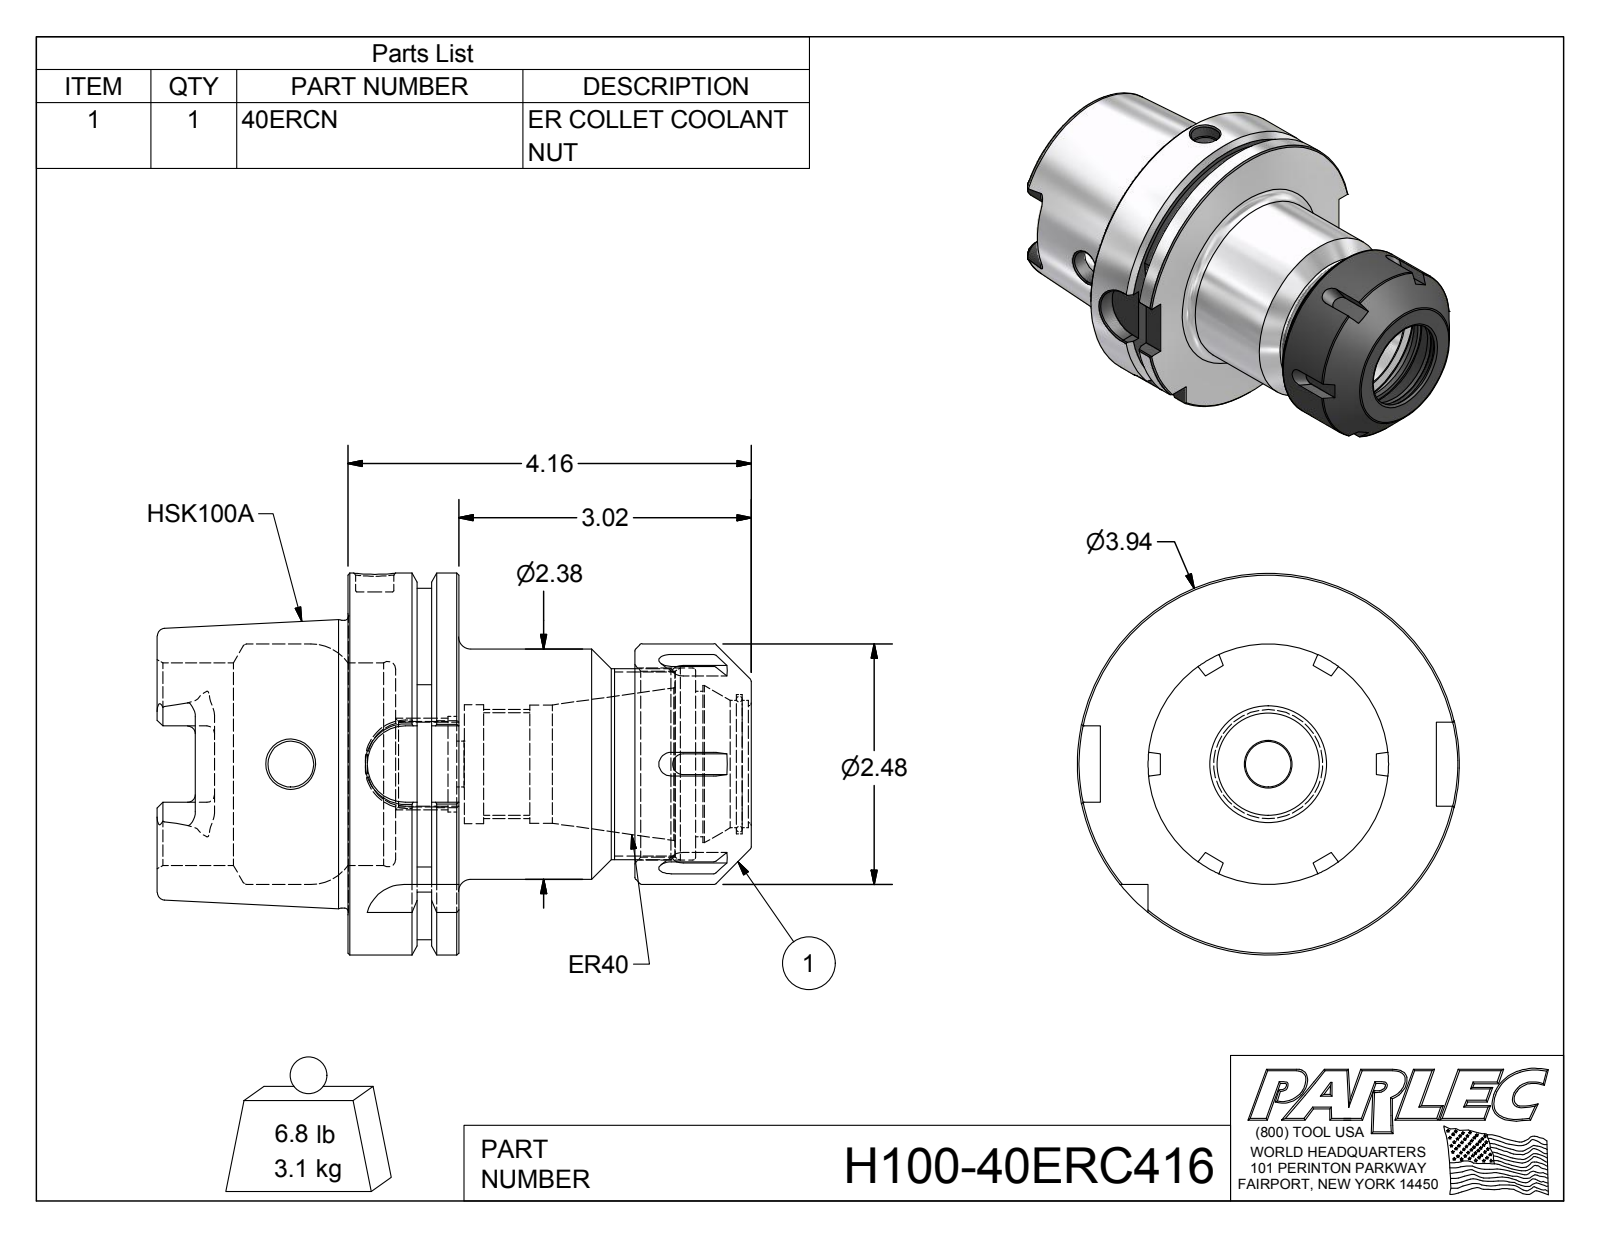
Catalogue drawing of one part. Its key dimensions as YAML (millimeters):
part_name: "H100-40ERC416; H100-40ER4-1; 40ERCN"
step_written_by: "Autodesk Inventor 2012 (AUTOMOTIVE_DESIGN)"
units: millimeters
bodies: {solids: 2, faces: 189, planar: 71, cylindrical: 44, other: 74}
overall_size: [155.7, 100, 100]
volume: 391200
surface_area: 79420
round_holes:
  - {diameter: 12, count: 2}
  - {diameter: 10, count: 1}
  - {diameter: 22.4, count: 1}
  - {diameter: 25, count: 1}
  - {diameter: 26.8, count: 1}
  - {diameter: 31, count: 1}
  - {diameter: 31.1, count: 1}
  - {diameter: 33.4, count: 1}
  - {diameter: 36.5, count: 1}
  - {diameter: 38.1, count: 1}
  - {diameter: 41.1, count: 1}
  - {diameter: 48.7, count: 1}
round_bosses_or_shafts:
  - {diameter: 100, count: 1}
  - {diameter: 75.4, count: 1}
  - {diameter: 63, count: 1}
  - {diameter: 60.3, count: 1}
  - {diameter: 50, count: 1}
partial_cylinders:
  - {radius: 2, count: 6}
  - {radius: 4.9, count: 4}
  - {radius: 10, count: 4}
  - {radius: 46, count: 1}
face_to_face_distances: [29, 12.5, 16.5, 50, 62.5, 79, 141.1, 91.1, 78.6, 62.1]
